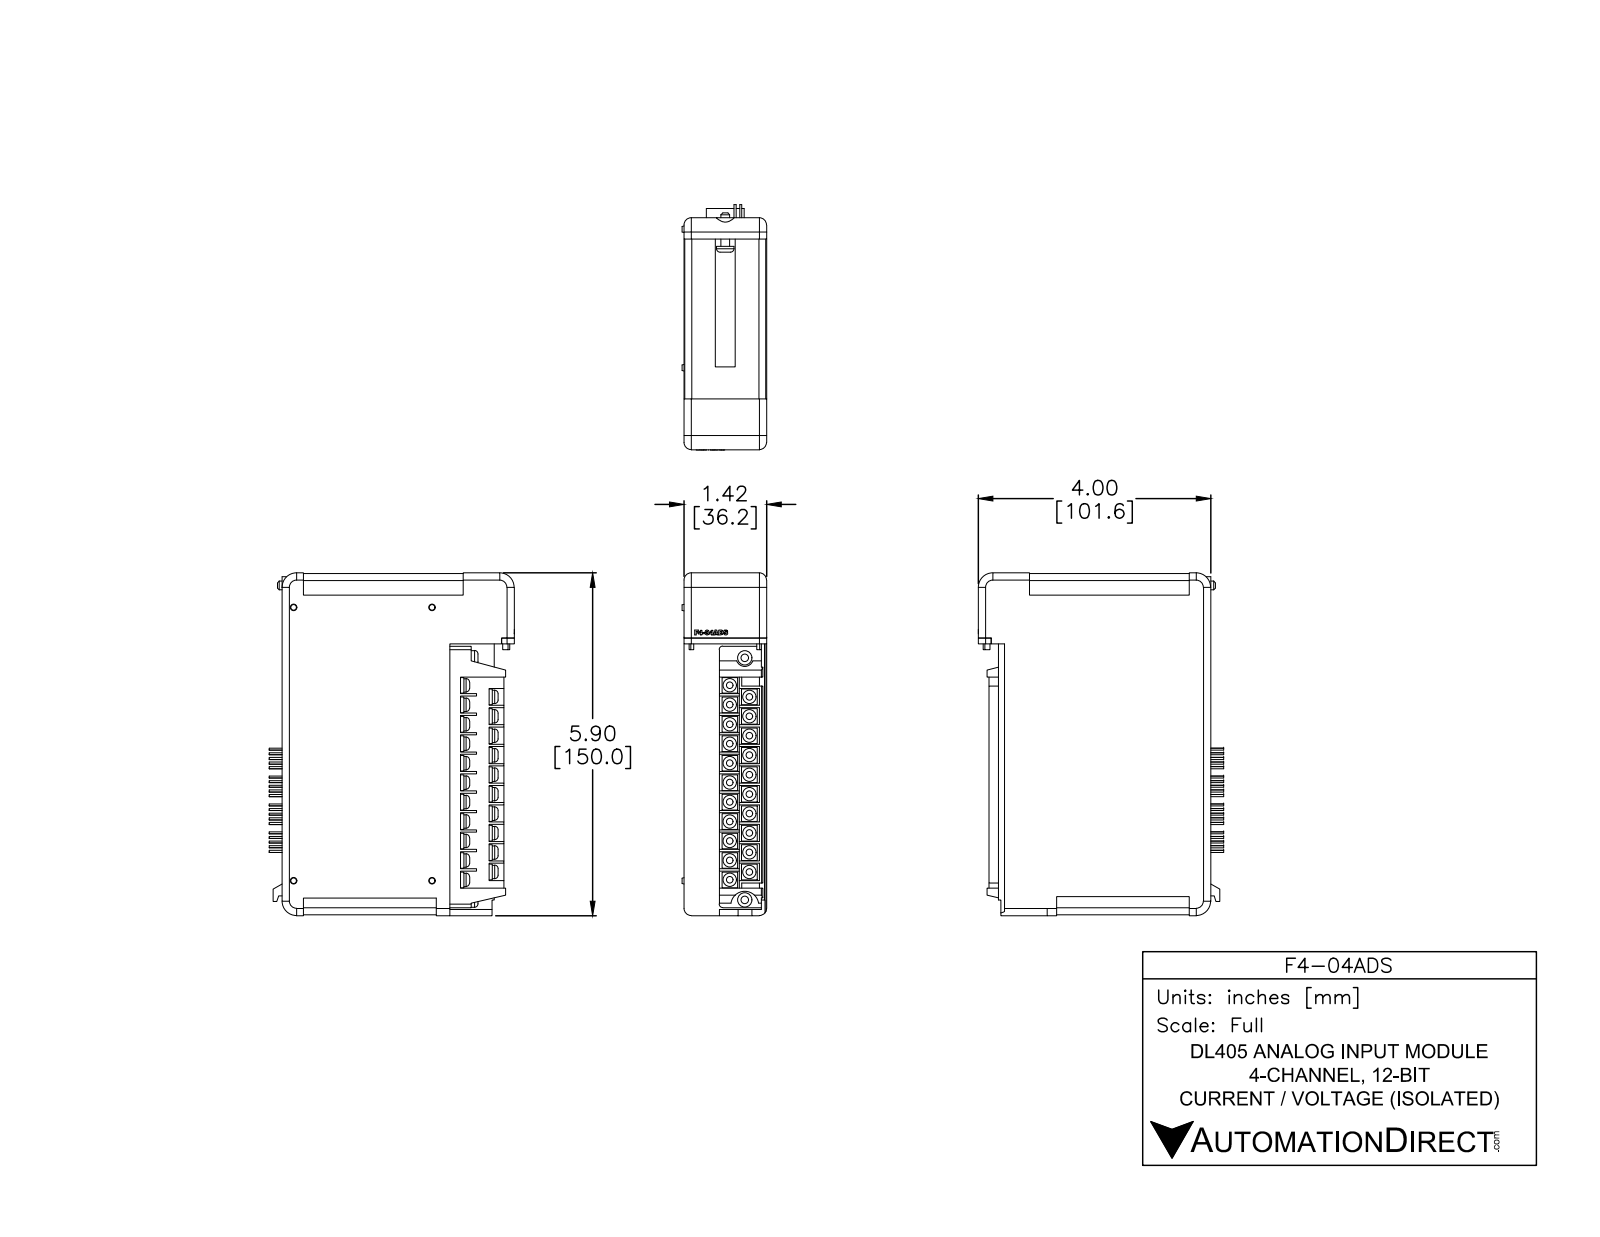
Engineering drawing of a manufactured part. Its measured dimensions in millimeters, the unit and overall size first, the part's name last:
Units: millimetres
Overall size (bounding box): 150 × 107.3 × 37
Round bosses / shafts (diameter × count): ⌀5.8 ×21, ⌀0.9 ×20, ⌀0.9 ×20, ⌀6.4 ×2, ⌀7.6 ×1, ⌀3.8 ×1
Partial cylindrical surfaces — rounded edges, fillets, slot ends (radius × count): R0.4 ×82, R3.2 ×8, R3 ×4, R6.4 ×3, R0.8 ×2, R1.5 ×2, R3.8 ×1, R3.8 ×1
Main face-to-face distances: 36.2, 0.4, 73.4, 149.2, 35.8, 11.9, 24.3, 149.6, 30.7, 8.8
Volume: 452 300 mm³ · Surface area: 58 370 mm²
Bodies: 6 solids, 901 faces (560 planar, 246 cylindrical, 95 other)
Part name (STEP PRODUCT): F4-04ADS
STEP written by: SolidWorks 2014 (AUTOMOTIVE_DESIGN)
